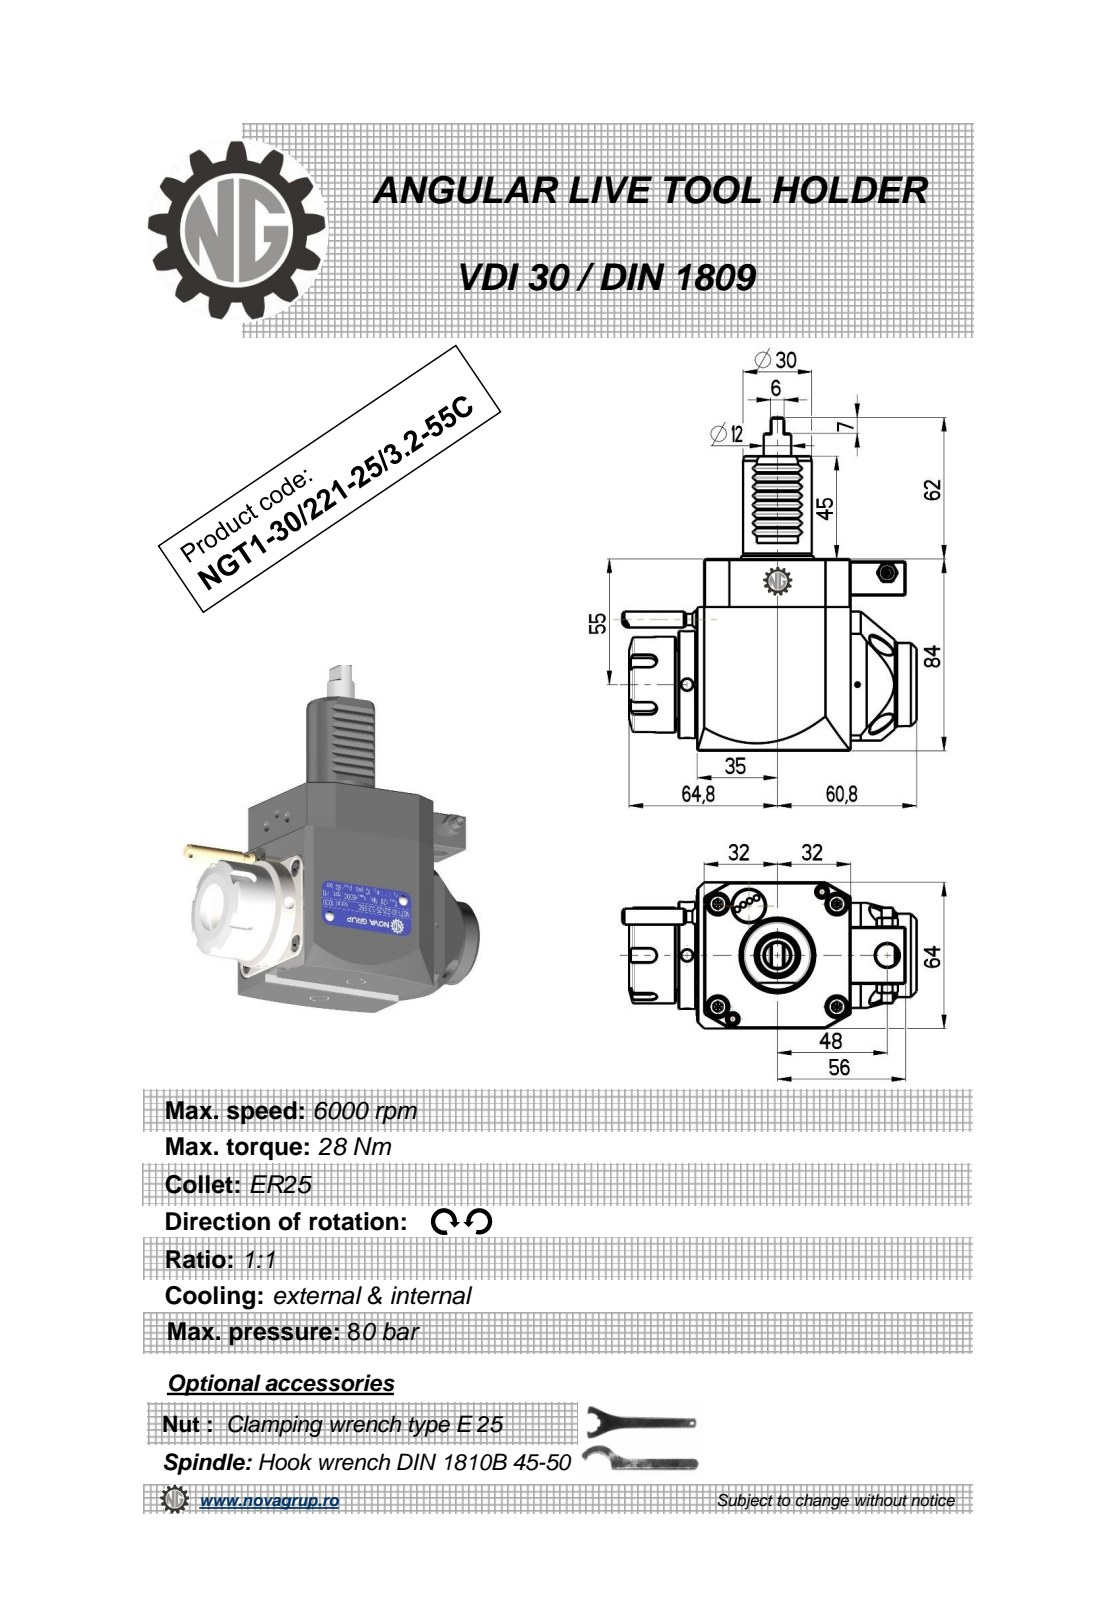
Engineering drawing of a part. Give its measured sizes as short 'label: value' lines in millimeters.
name: NGT1_30_221_25_3_2_55C
written by: PRO/ENGINEER BY PARAMETRIC TECHNOLOGY CORPORATION, 2010280 (CONFIG_CONTROL_DESIGN)
unit: mm
bodies: 1 solid, 414 faces (186 planar, 82 cylindrical, 146 other)
size: 146 × 128.63 × 64
volume: 472 549 mm³; area: 48 513 mm²
holes: 2× ⌀5, 1× ⌀2.5, 1× ⌀3, 1× ⌀4.2, 1× ⌀9.5, 1× ⌀10, 1× ⌀20.3
bosses: 2× ⌀8.96, 2× ⌀5, 1× ⌀47, 1× ⌀42, 1× ⌀36.5, 1× ⌀35, 1× ⌀30, 1× ⌀12
rounds: 12× R0.26, 8× R0.3, 5× R3, 2× R0.8, 2× R160, 1× R32
face distances: 64, 84, 0.5, 67.2, 7.5, 67, 3.2, 3, 8, 46
hole spacings: 24.76, 33.19, 46.5, 87.45, 100.24
